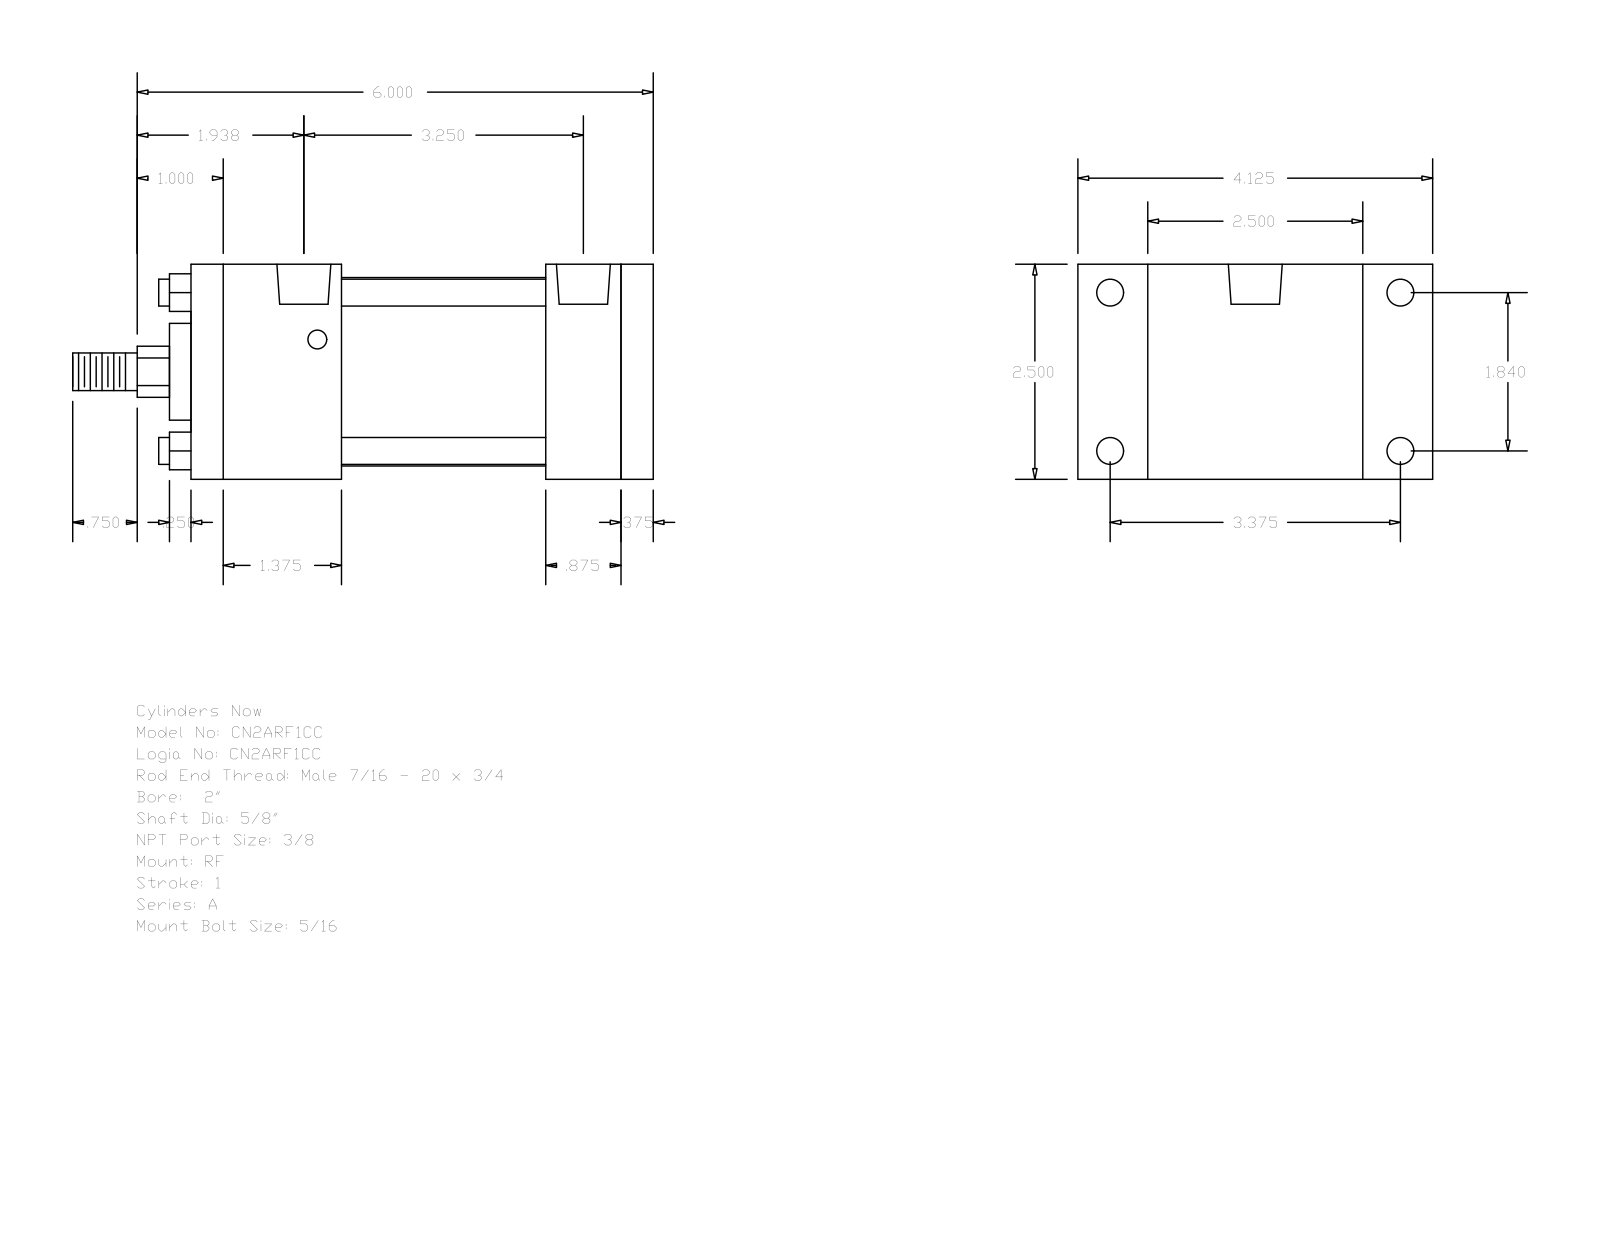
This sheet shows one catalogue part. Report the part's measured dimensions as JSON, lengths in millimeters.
{"part_name": "A_RF__0200_0.625", "step_written_by": "GSSL Pune (CONFIG_CONTROL_DESIGN)", "units": "millimeters", "bodies": {"solids": 0, "faces": 92, "planar": 64, "cylindrical": 28, "other": 0}, "overall_size": [171.45, 104.78, 63.5], "round_holes": [[5.56, 4], [7.94, 4], [15.93, 2]], "round_bosses_or_shafts": [[7.94, 4], [55.63, 1], [28.57, 1], [15.88, 1], [11.11, 1]], "partial_cylinders_radius": [[7.54, 1]], "face_to_face_distances": [63.5, 136.52, 127, 9.52, 44.45, 82.55, 92.07, 104.77, 60.32, 22.23], "hole_center_spacings": [46.74, 74.6, 85.72, 97.63, 3.97, 3.98, 78.57, 78.58]}
